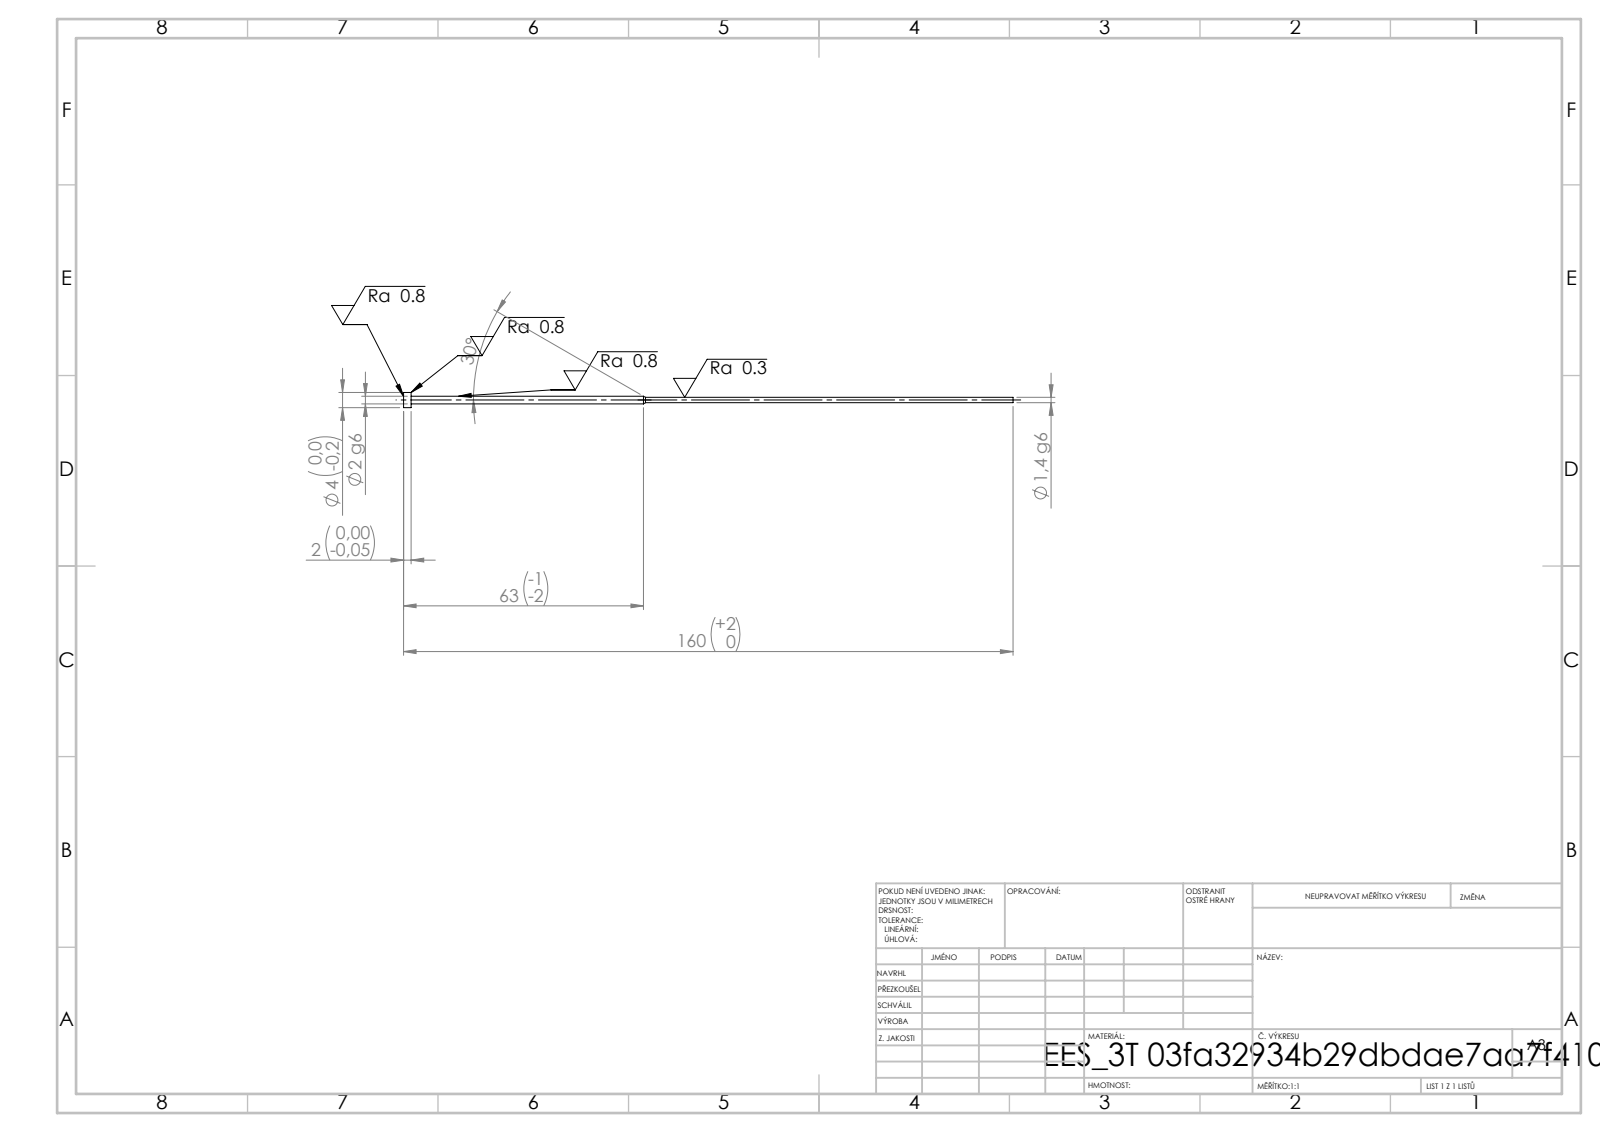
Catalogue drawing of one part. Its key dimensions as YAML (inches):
step_written_by: "SolidWorks 2019 (CONFIG_CONTROL_DESIGN)"
units: inches
bodies: {solids: 1, faces: 11, planar: 3, cylindrical: 6, other: 2}
overall_size: [6.299, 0.157, 0.157]
volume: 0.022
surface_area: 1.33
round_bosses_or_shafts:
  - {diameter: 0.157, count: 1}
  - {diameter: 0.079, count: 1}
  - {diameter: 0.055, count: 1}
face_to_face_distances: [0.079, 6.22, 6.299]
